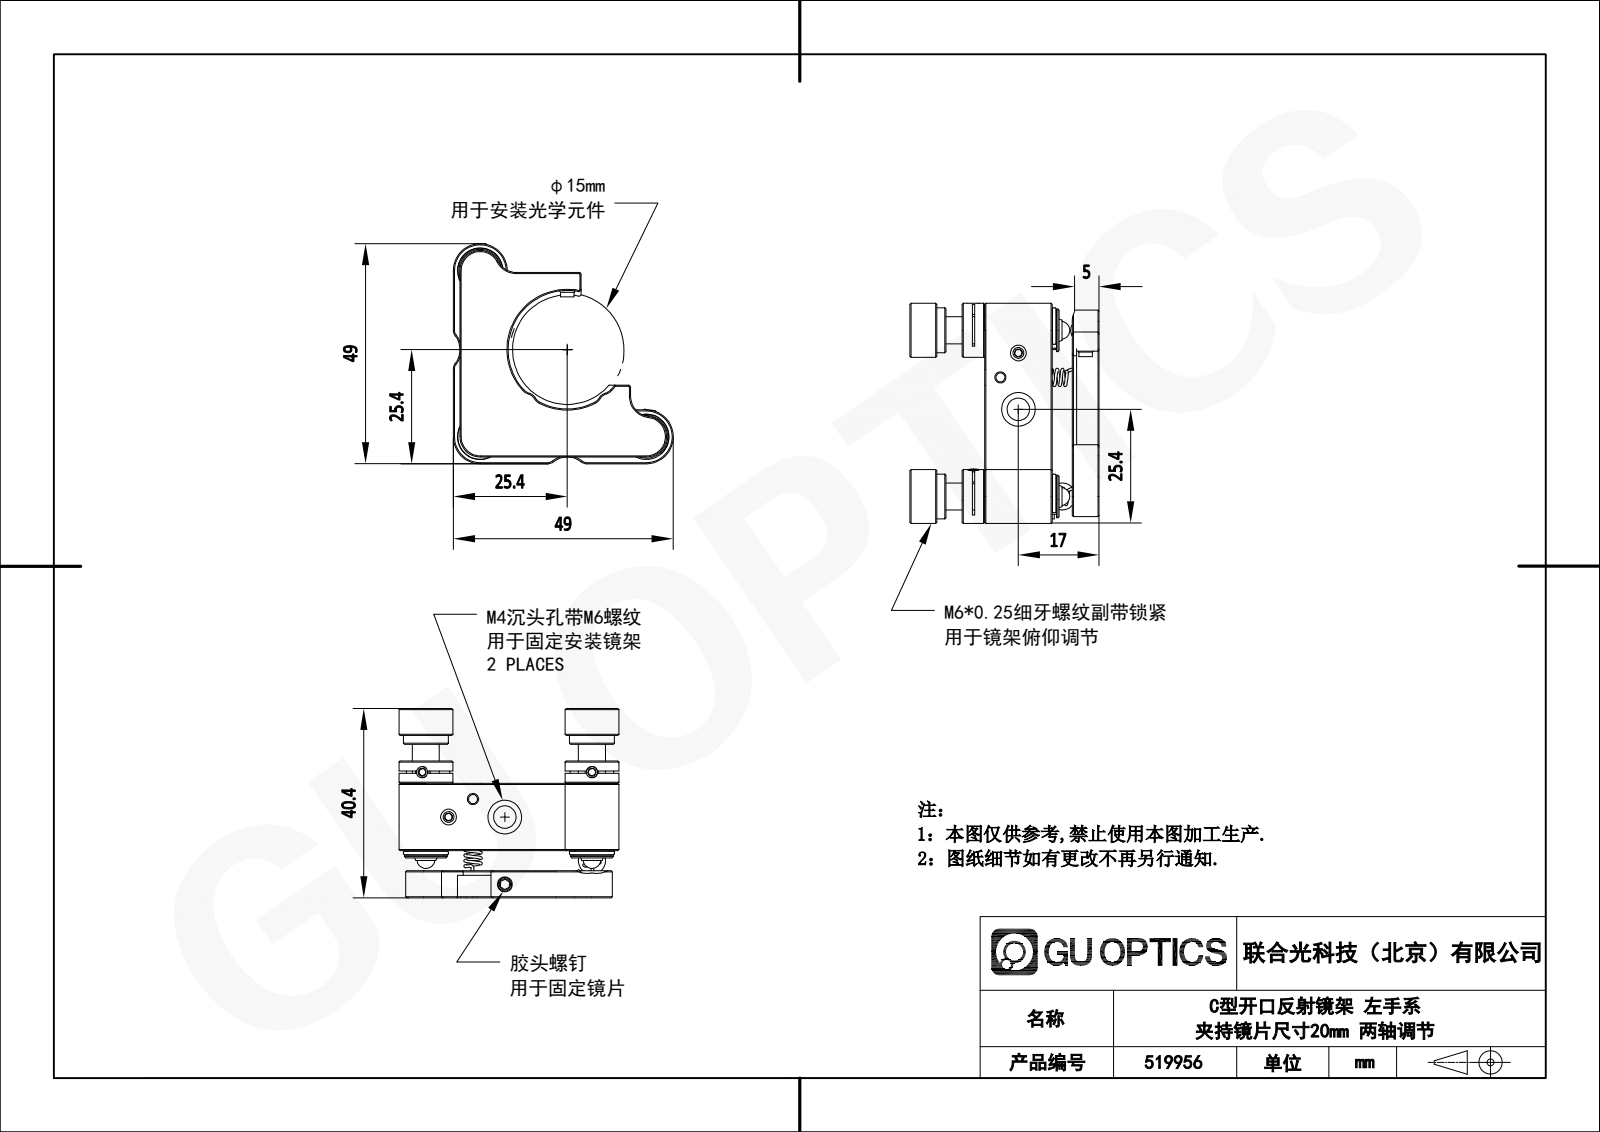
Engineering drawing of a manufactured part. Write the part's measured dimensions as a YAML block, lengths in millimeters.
step_written_by: "SolidWorks 2021 (CONFIG_CONTROL_DESIGN)"
units: millimeters
bodies: {solids: 0, faces: 505, planar: 157, cylindrical: 130, other: 218}
overall_size: [49, 49, 40.68]
round_holes:
  - {diameter: 6, count: 3}
  - {diameter: 2.5, count: 2}
  - {diameter: 4, count: 2}
  - {diameter: 5, count: 2}
  - {diameter: 7.5, count: 2}
  - {diameter: 3.3, count: 1}
  - {diameter: 5.1, count: 1}
round_bosses_or_shafts:
  - {diameter: 3, count: 7}
  - {diameter: 10, count: 3}
  - {diameter: 9.5, count: 3}
  - {diameter: 12, count: 2}
  - {diameter: 8, count: 2}
  - {diameter: 4, count: 2}
  - {diameter: 8.9, count: 1}
  - {diameter: 6, count: 1}
partial_cylinders:
  - {radius: 4.5, count: 6}
  - {radius: 0.2, count: 4}
  - {radius: 0.5, count: 4}
  - {radius: 2, count: 4}
  - {radius: 2.5, count: 4}
  - {radius: 1.25, count: 2}
  - {radius: 5, count: 2}
  - {radius: 10, count: 2}
face_to_face_distances: [6, 25, 19, 4, 10, 15, 1.5, 5, 2.25, 2.75]
hole_center_spacings: [8.15, 10.5, 45.51, 14.5, 19.82, 37.48, 52.33]
